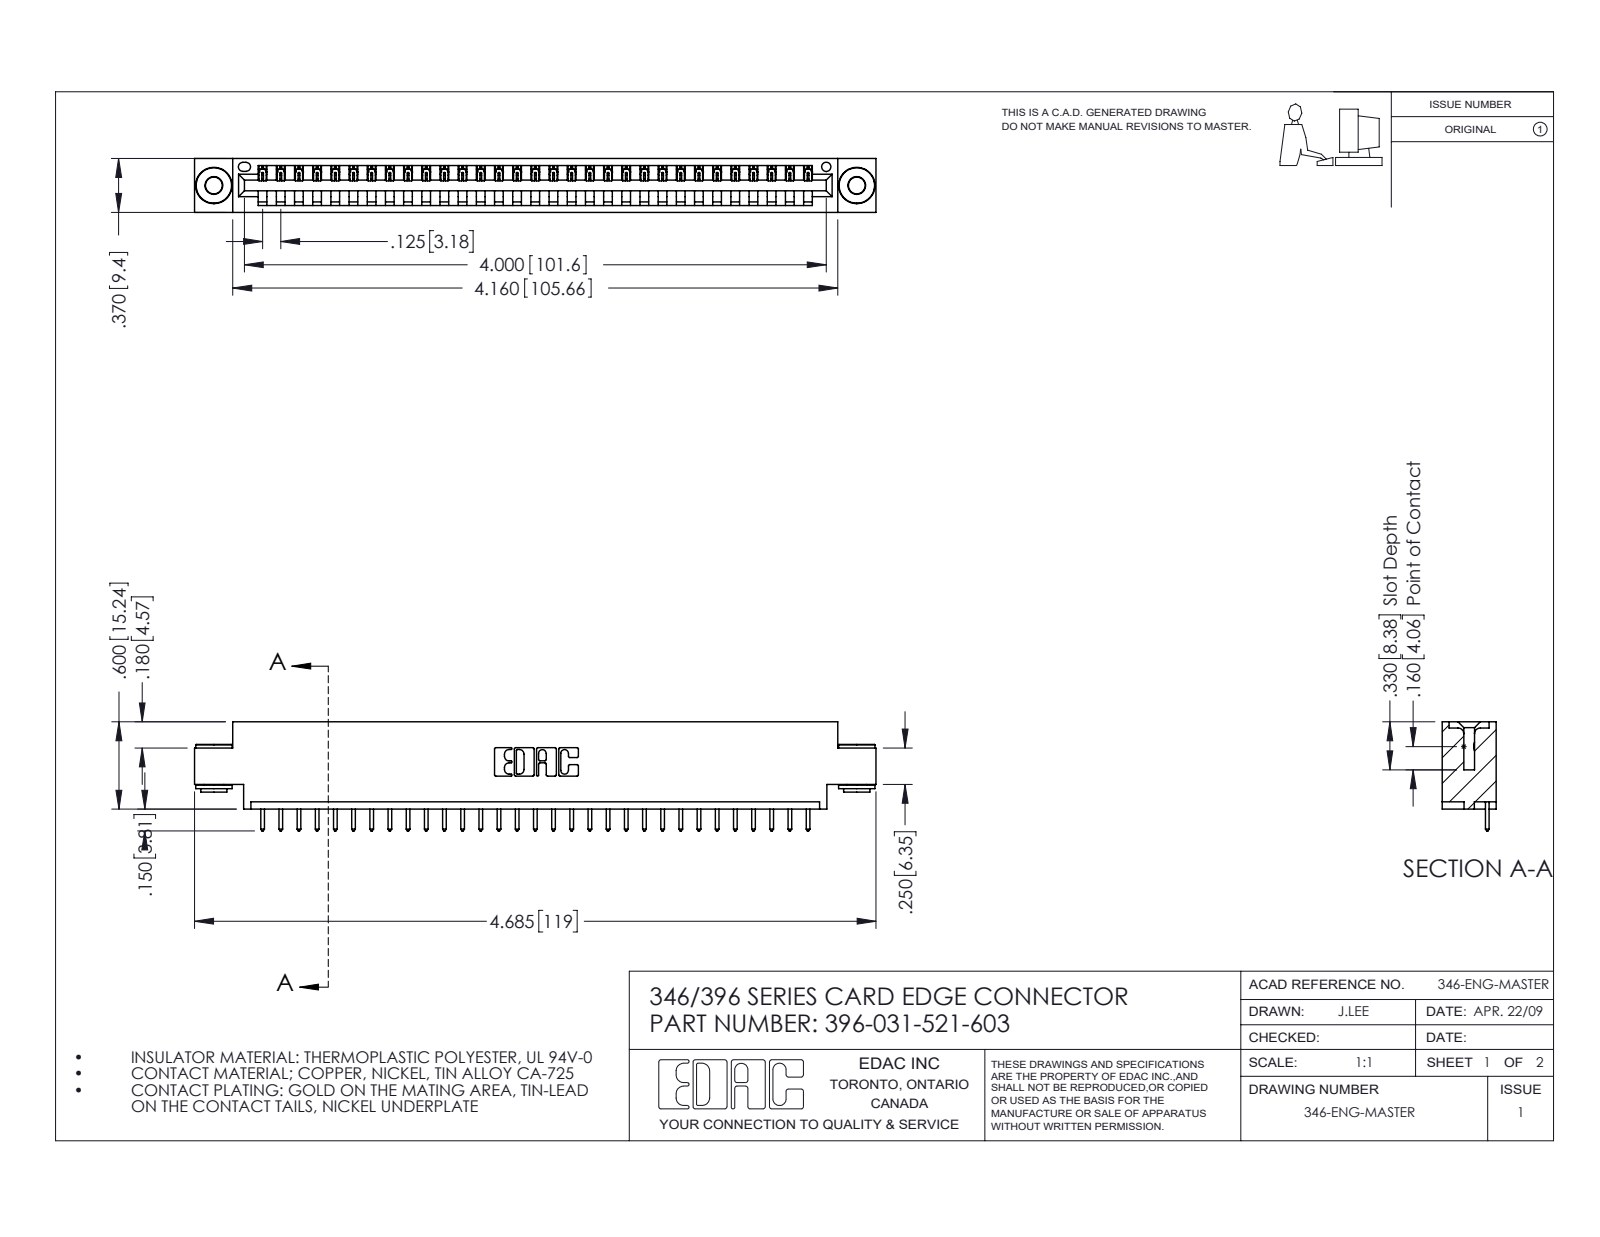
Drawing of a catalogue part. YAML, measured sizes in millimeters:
part_name: "346 Part_0.170 Offset - 0.156 Dia-TH; 396-031-521-603; 345-250-002_345-250-002-102; 345-292-001_345-293-121"
step_written_by: "SolidWorks 2016 (CONFIG_CONTROL_DESIGN)"
units: millimeters
bodies: {solids: 34, faces: 1962, planar: 1330, cylindrical: 624, other: 8}
overall_size: [119, 19.1, 9.4]
volume: 11100
surface_area: 13770
round_holes:
  - {diameter: 2.9, count: 2}
  - {diameter: 4, count: 2}
  - {diameter: 1.6, count: 1}
round_bosses_or_shafts:
  - {diameter: 6.4, count: 2}
  - {diameter: 4.6, count: 2}
  - {diameter: 3.5, count: 2}
partial_cylinders:
  - {radius: 0.2, count: 62}
  - {radius: 0.3, count: 62}
  - {radius: 0.3, count: 22}
  - {radius: 0.2, count: 6}
  - {radius: 0.8, count: 6}
  - {radius: 0.7, count: 3}
  - {radius: 0.8, count: 2}
  - {radius: 1, count: 2}
face_to_face_distances: [1.2, 8.2, 9.4, 6.4, 0.6, 1.8, 7.6, 3.8, 5.6, 2.5]
hole_center_spacings: [6.2, 107, 112.3]
